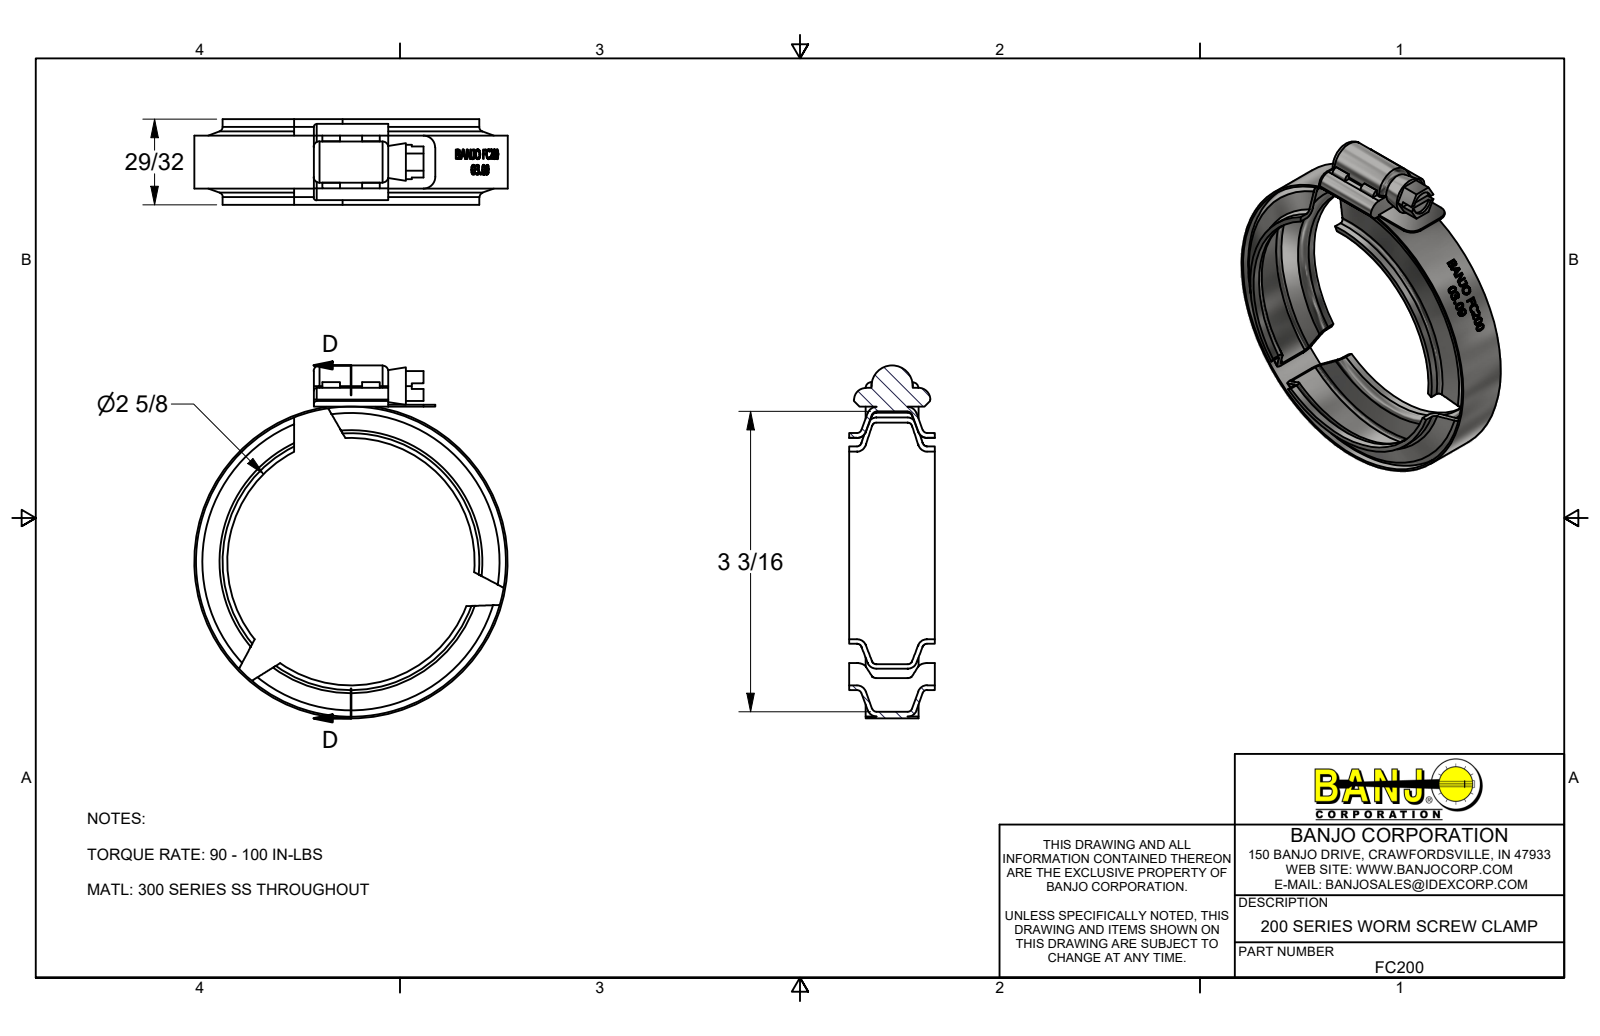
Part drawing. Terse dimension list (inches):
name: FC200
written by: Autodesk Inventor 2014 (AUTOMOTIVE_DESIGN)
unit: in
bodies: 1 solid, 386 faces (131 planar, 58 cylindrical, 197 other)
size: 3.747 × 3.33 × 0.91
volume: 0.862 in³; area: 30.7 in²
holes: 1× ⌀0.25, 1× ⌀2.628, 1× ⌀3.19, 1× ⌀3.29
bosses: 1× ⌀3.33, 1× ⌀2.728
rounds: 4× R0.06, 4× R0.125, 3× R0.03, 1× R0.219, 1× R1.655
face distances: 0.174, 0.737, 0.91, 0.02, 0.563, 0.79, 0.317, 0.999, 0.209, 0.129
